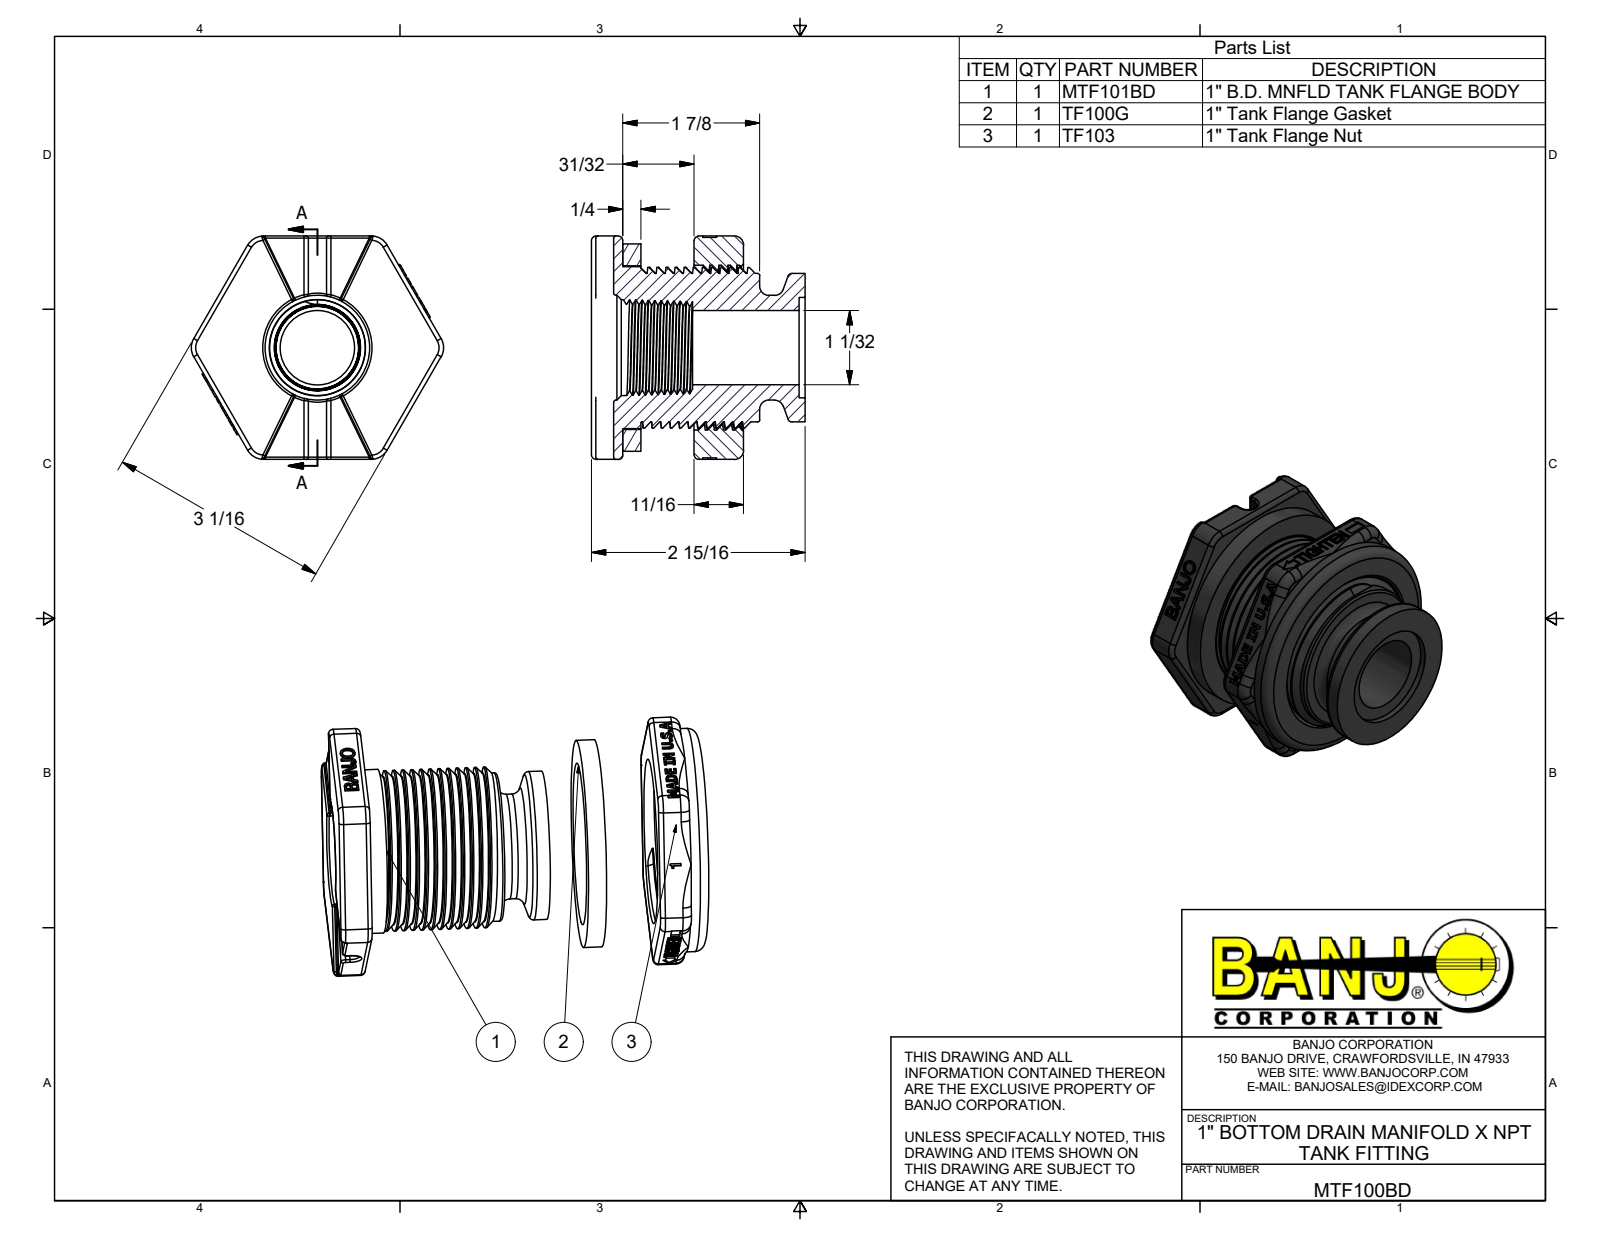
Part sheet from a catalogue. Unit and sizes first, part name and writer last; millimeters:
Units: millimetres
Overall size (bounding box): 88.08 × 77.98 × 74.61
Round holes (diameter × count): ⌀25.91 ×1, ⌀35.05 ×1, ⌀36.58 ×1, ⌀53.85 ×1, ⌀56.52 ×1, ⌀57.53 ×1
Round bosses / shafts (diameter × count): ⌀77.98 ×1, ⌀72.39 ×1, ⌀57.15 ×1, ⌀56.08 ×1, ⌀51.82 ×1
Partial cylindrical surfaces — rounded edges, fillets, slot ends (radius × count): R0.76 ×18, R1.52 ×12, R3.17 ×7, R1.59 ×6, R6.35 ×6, R0.38 ×4, R10 ×1, R15.09 ×1
Main face-to-face distances: 10.92, 35.81, 24.89, 6.35, 18.54, 17.27, 35.82, 77.98, 53.09, 42.17
Volume: 191 503 mm³ · Surface area: 58 032 mm²
Bodies: 3 solids, 847 faces (481 planar, 102 cylindrical, 264 other)
Part name (STEP PRODUCT): MTF100BD; MTF101BD; TF103; TF103X (+1 more)
STEP written by: Autodesk Inventor 2017 (AUTOMOTIVE_DESIGN)
